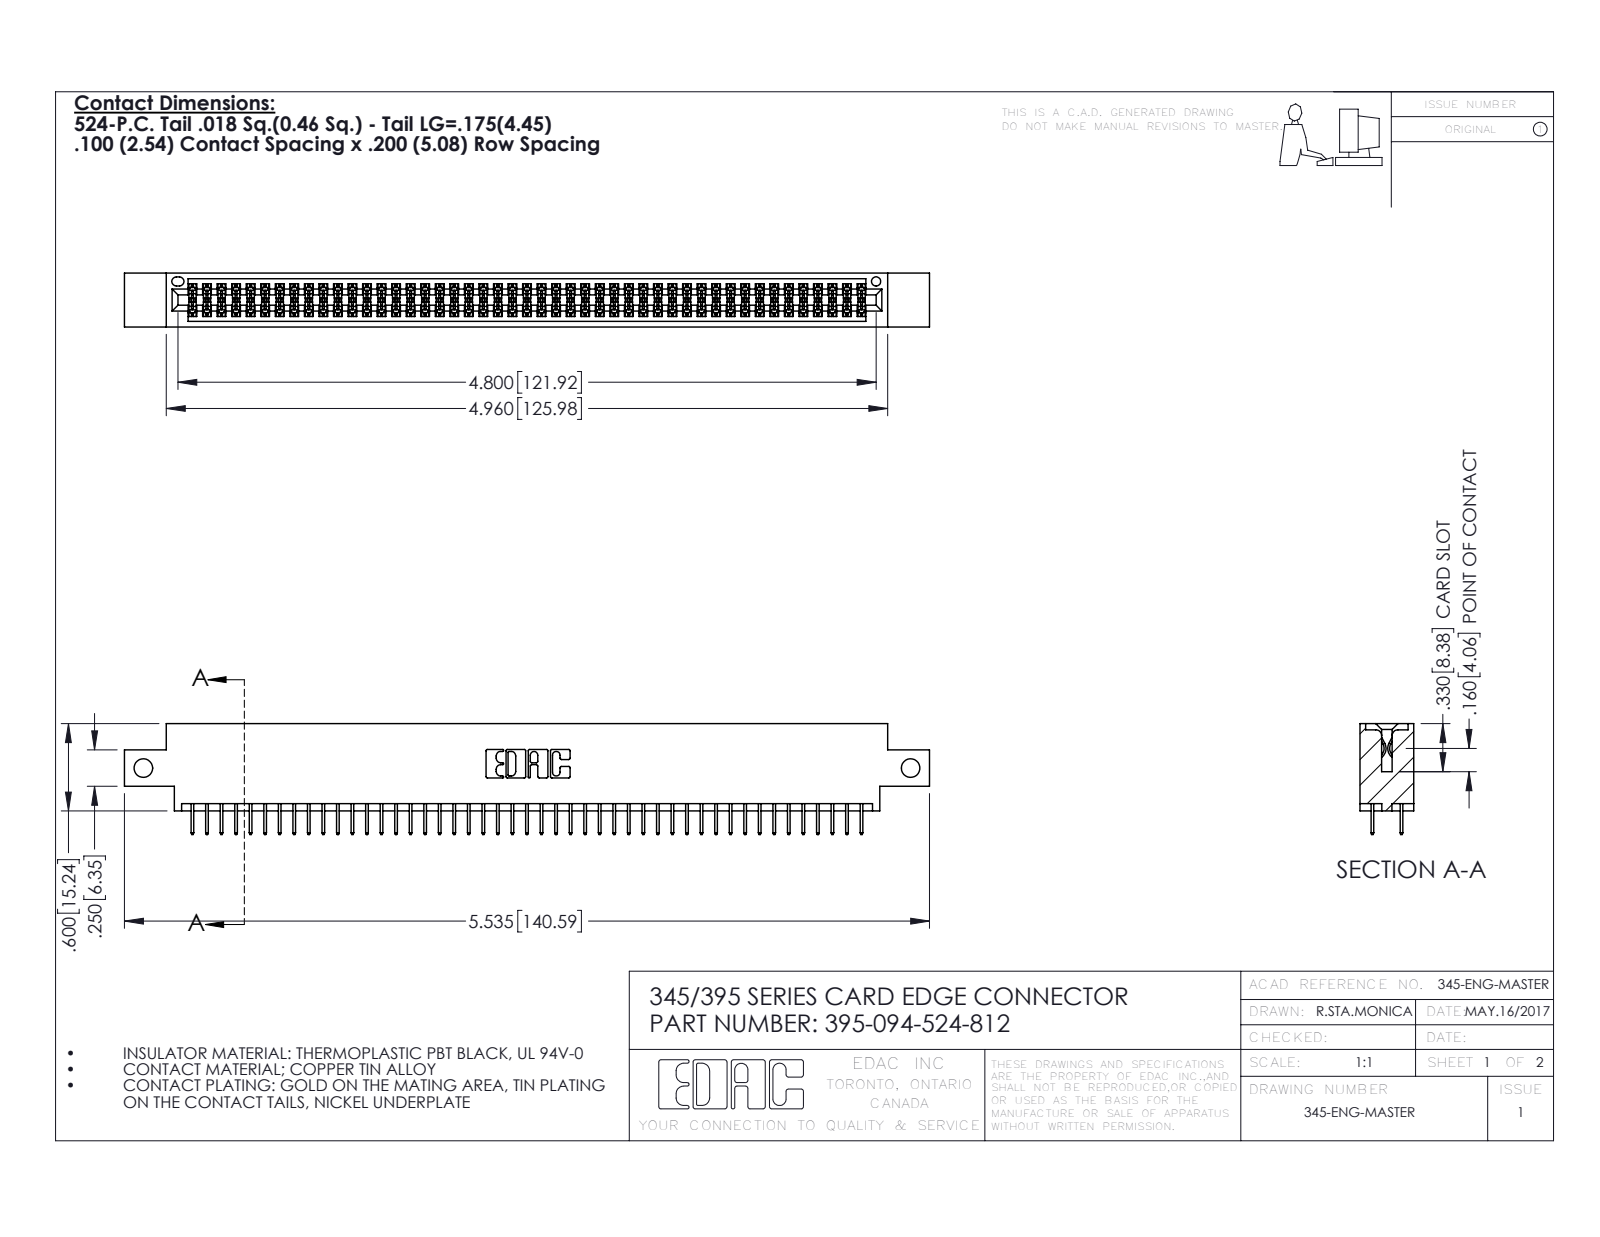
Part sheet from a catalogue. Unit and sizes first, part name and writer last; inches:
Units: inches
Overall size (bounding box): 5.535 × 0.762 × 0.37
Round holes (diameter × count): ⌀0.128 ×2, ⌀0.064 ×1
Partial cylindrical surfaces — rounded edges, fillets, slot ends (radius × count): R0.006 ×141, R0.01 ×22, R0.007 ×6, R0.031 ×6, R0.026 ×3, R0.014 ×2, R0.019 ×2, R0.022 ×2
Main face-to-face distances: 0.072, 0.298, 0.37, 0.2, 0.098, 0.272, 0.025, 0.225, 0.175, 0.072
Hole centre spacings: 5.275
Volume: 0.815 in³ · Surface area: 30.19 in²
Bodies: 95 solids, 5206 faces (3750 planar, 1456 cylindrical, 0 other)
Part name (STEP PRODUCT): 345 Part_0.170 Offset - Side Mount; 345-292-001_345-293-124; 395-094-524-812
STEP written by: SolidWorks 2016 (CONFIG_CONTROL_DESIGN)
